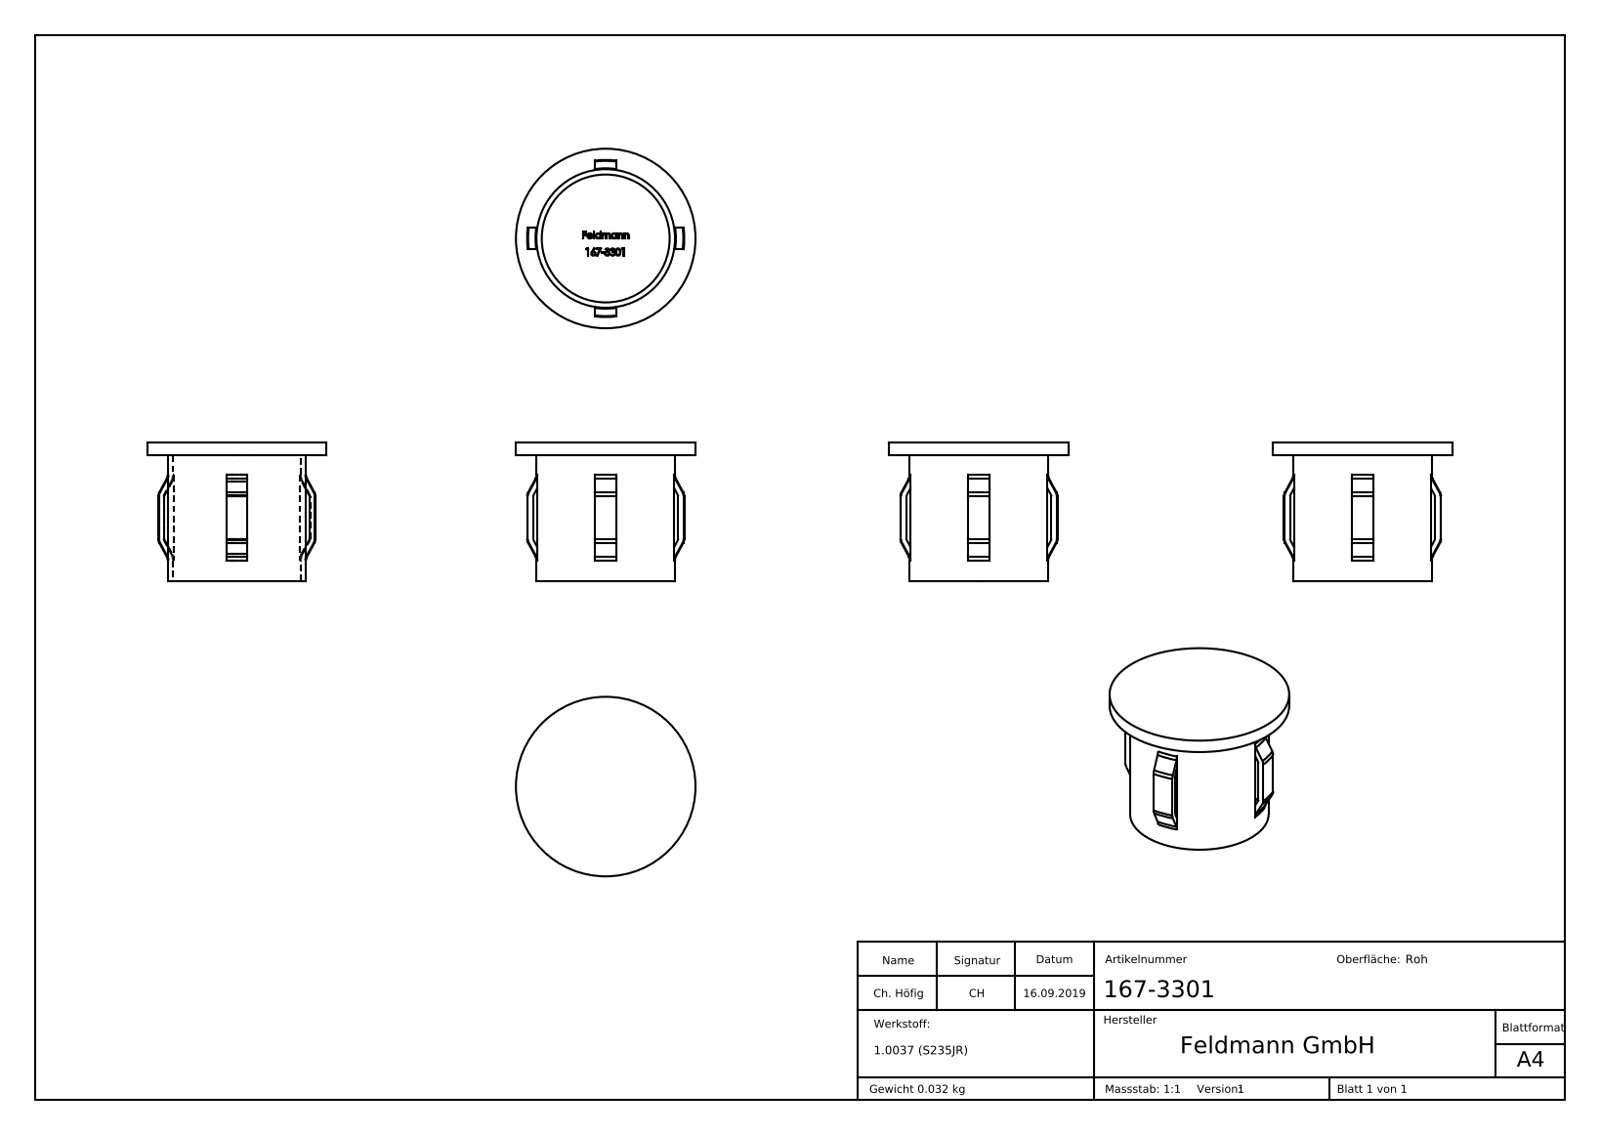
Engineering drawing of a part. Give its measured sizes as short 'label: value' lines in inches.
name: 167-3301
written by: SolidWorks 2015 (CONFIG_CONTROL_DESIGN)
unit: in
bodies: 1 solid, 296 faces (126 planar, 16 cylindrical, 154 other)
size: 1.327 × 1.327 × 1.031
volume: 0.25 in³; area: 9.334 in²
holes: 1× ⌀0.945
bosses: 1× ⌀1.327, 1× ⌀1.024
rounds: 1× R0.541, 1× R0.581
face distances: 0.098, 0.157, 0.933, 1.031, 0.094, 0.937, 0.117, 0.079, 0.015, 0.05
